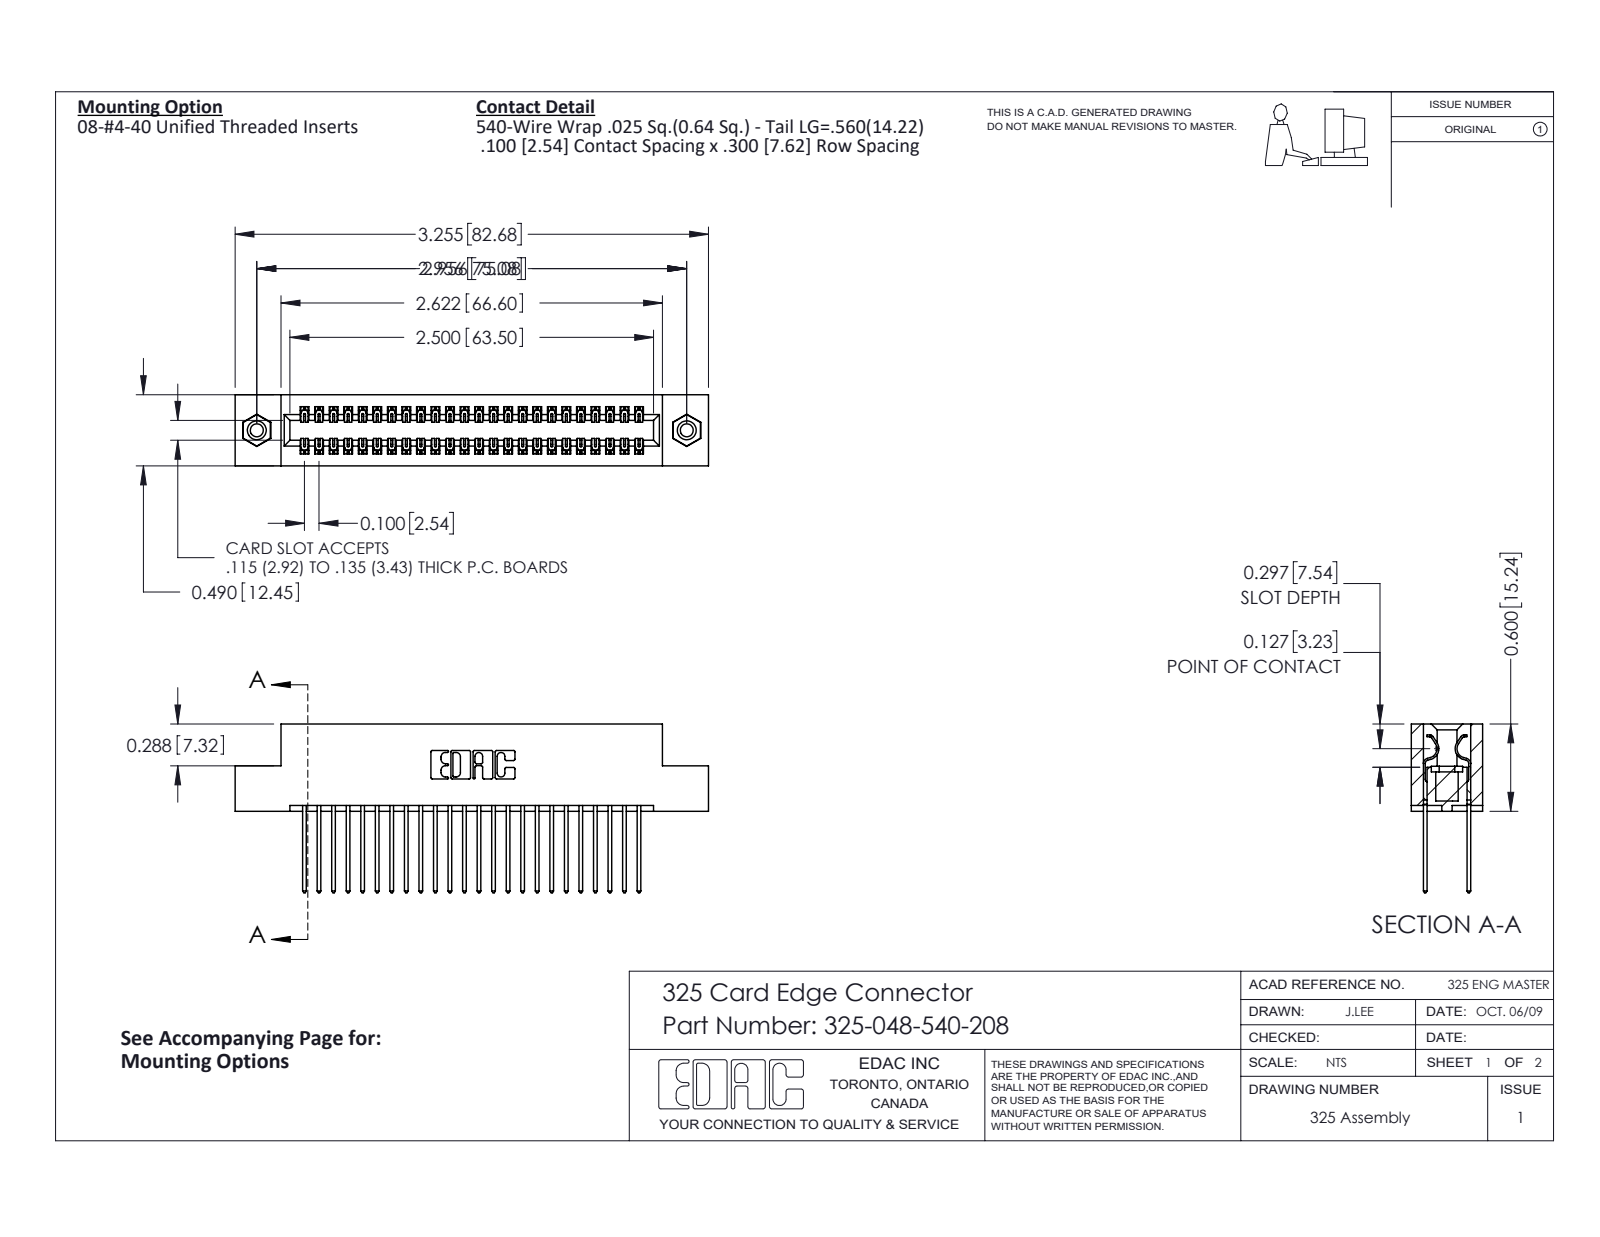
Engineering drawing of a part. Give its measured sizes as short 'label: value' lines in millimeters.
name: 325 Part_TI; 345-250-001_345-250-003-102; 325-048-540-208; 325-292-001_325-293-140
written by: SolidWorks 2016 (CONFIG_CONTROL_DESIGN)
unit: mm
bodies: 51 solids, 2670 faces (1830 planar, 824 cylindrical, 16 other)
size: 82.7 × 29.5 × 12.4
volume: 10 700 mm³; area: 13 390 mm²
holes: 2× ⌀2.3, 2× ⌀3.2, 2× ⌀4.1
bosses: 2× ⌀3.9
rounds: 72× R0.2, 48× R0.3, 22× R0.3, 6× R0.2, 6× R0.8, 3× R0.7, 2× R0.4, 2× R0.6
face distances: 2.1, 10.3, 7.6, 2.7, 9.7, 0.6, 12.4, 8.3, 7, 1
hole spacings: 75.1
